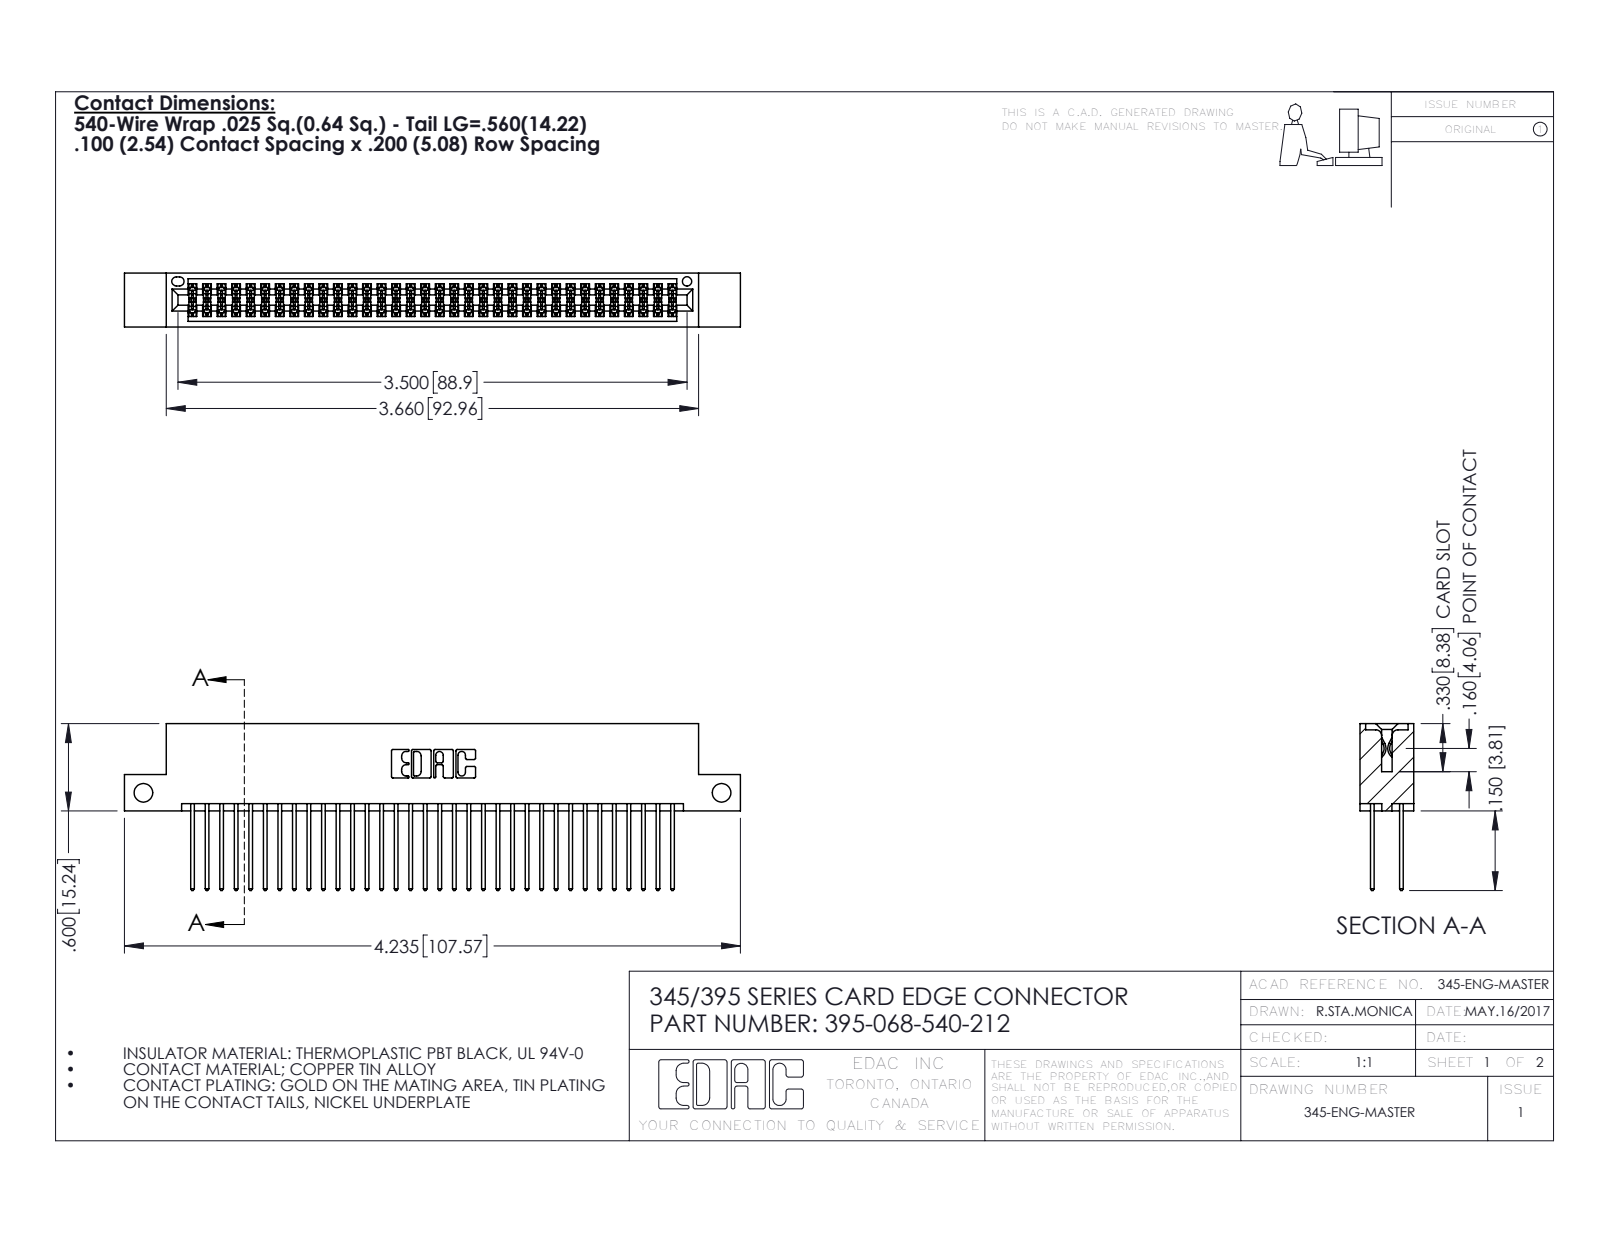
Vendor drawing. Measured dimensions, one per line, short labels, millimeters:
name: 345 Part_Flush Mounting Lugs - Side Mount; 395-068-540-212; 345-292-001_345-293-140
written by: SolidWorks 2016 (CONFIG_CONTROL_DESIGN)
unit: mm
bodies: 69 solids, 3526 faces (2324 planar, 1202 cylindrical, 0 other)
size: 107.6 × 29.1 × 9.4
volume: 10 600 mm³; area: 16 500 mm²
holes: 2× ⌀3.3, 1× ⌀1.6
rounds: 102× R0.2, 68× R0.3, 22× R0.3, 6× R0.2, 6× R0.8, 3× R0.7, 2× R0.4, 2× R0.5
face distances: 7.6, 1.8, 5.1, 2.5, 6.9, 0.6, 9.4, 5.7, 4.4, 3.8
hole spacings: 101
